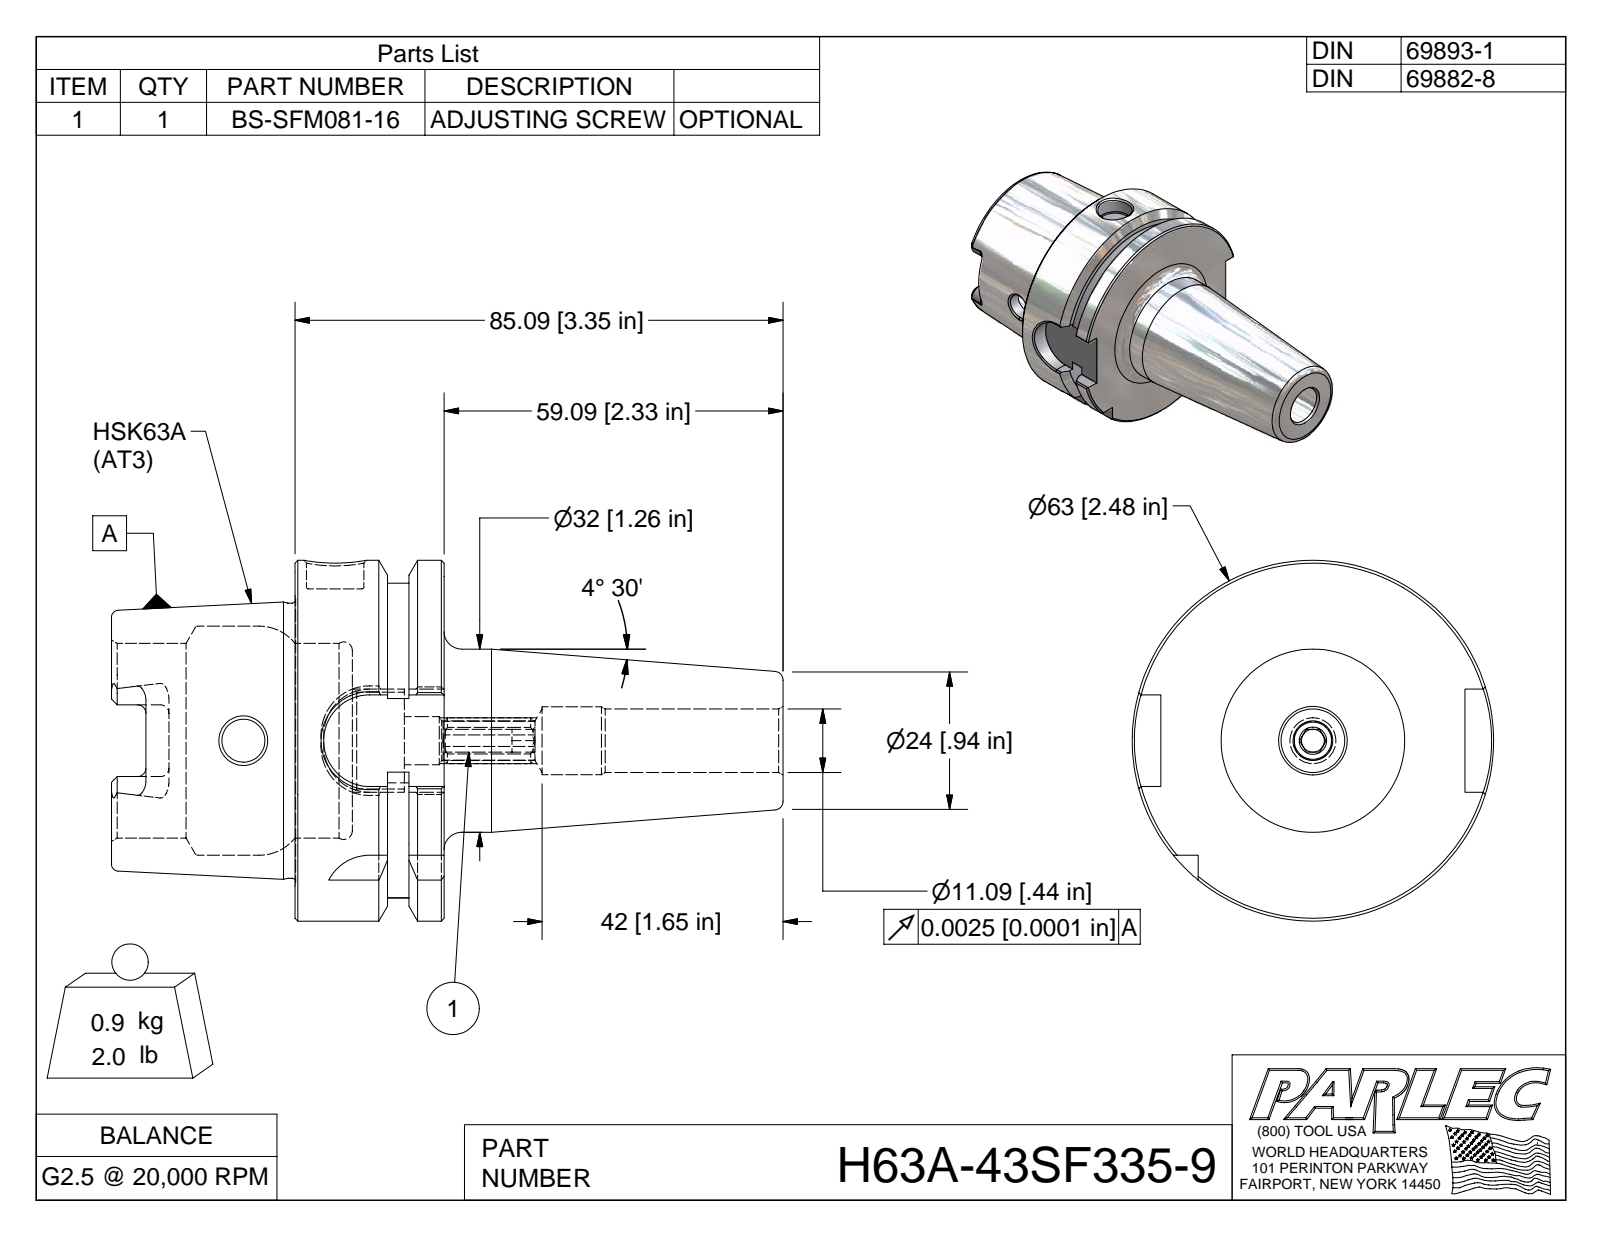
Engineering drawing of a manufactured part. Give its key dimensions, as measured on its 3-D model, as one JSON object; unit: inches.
{"part_name": "H63A-43SF335-9; H63A-43SF335-9-1; BS-SFM081-16", "step_written_by": "Autodesk Inventor 2009 (AUTOMOTIVE_DESIGN)", "units": "inches", "bodies": {"solids": 2, "faces": 157, "planar": 58, "cylindrical": 35, "other": 64}, "overall_size": [4.61, 2.48, 2.48], "volume_in3": 7.058, "surface_area_in2": 45.89, "round_holes": [[0.295, 1], [0.394, 1], [0.437, 1], [0.467, 1], [0.666, 1], [1.339, 1], [1.575, 1]], "round_bosses_or_shafts": [[2.48, 1], [1.891, 1], [1.26, 1]], "partial_cylinders_radius": [[0.059, 6], [0.113, 4], [0.315, 4], [0.157, 1], [1.083, 1]], "face_to_face_distances": [1.024, 0.241, 0.389, 0.394, 0.63, 1.26, 1.654, 2.283, 1.894, 0.635]}
